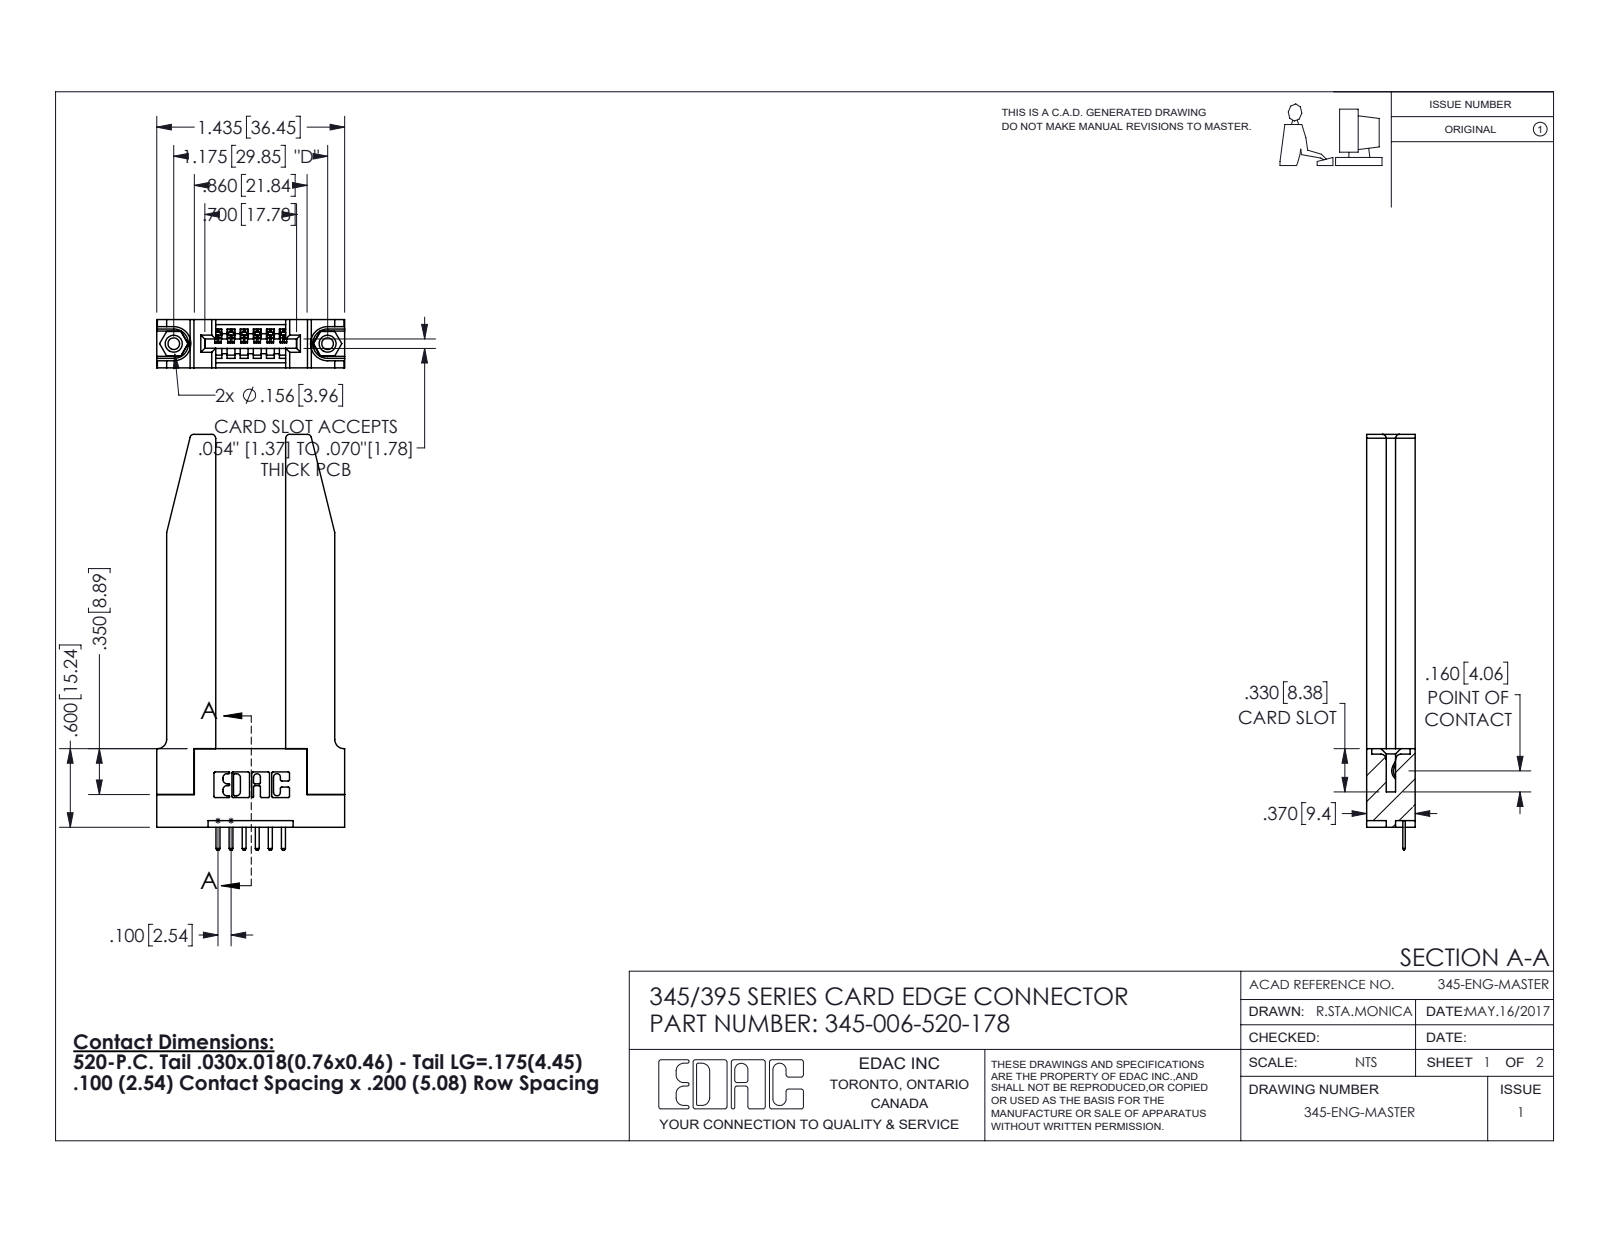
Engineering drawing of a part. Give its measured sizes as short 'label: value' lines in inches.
name: 345-220-078_345-220-078; 345-006-520-178; 345-292-001_345-293-120; 345-250-001_345-250-001-102 (+1 more)
written by: SolidWorks 2016 (CONFIG_CONTROL_DESIGN)
unit: in
bodies: 11 solids, 732 faces (474 planar, 206 cylindrical, 52 other)
size: 3.175 × 1.436 × 0.37
volume: 0.667 in³; area: 16.26 in²
holes: 2× ⌀0.089, 2× ⌀0.125, 2× ⌀0.156, 1× ⌀0.064
bosses: 2× ⌀0.155
rounds: 22× R0.01, 14× R0.01, 12× R0.006, 8× R0.03, 6× R0.007, 6× R0.031, 3× R0.026, 2× R0.031
face distances: 0.37, 0.15, 0.22, 0.535, 0.072, 0.148, 0.077, 0.298, 0.2, 0.095
hole spacings: 0.27, 0.946, 1.175
